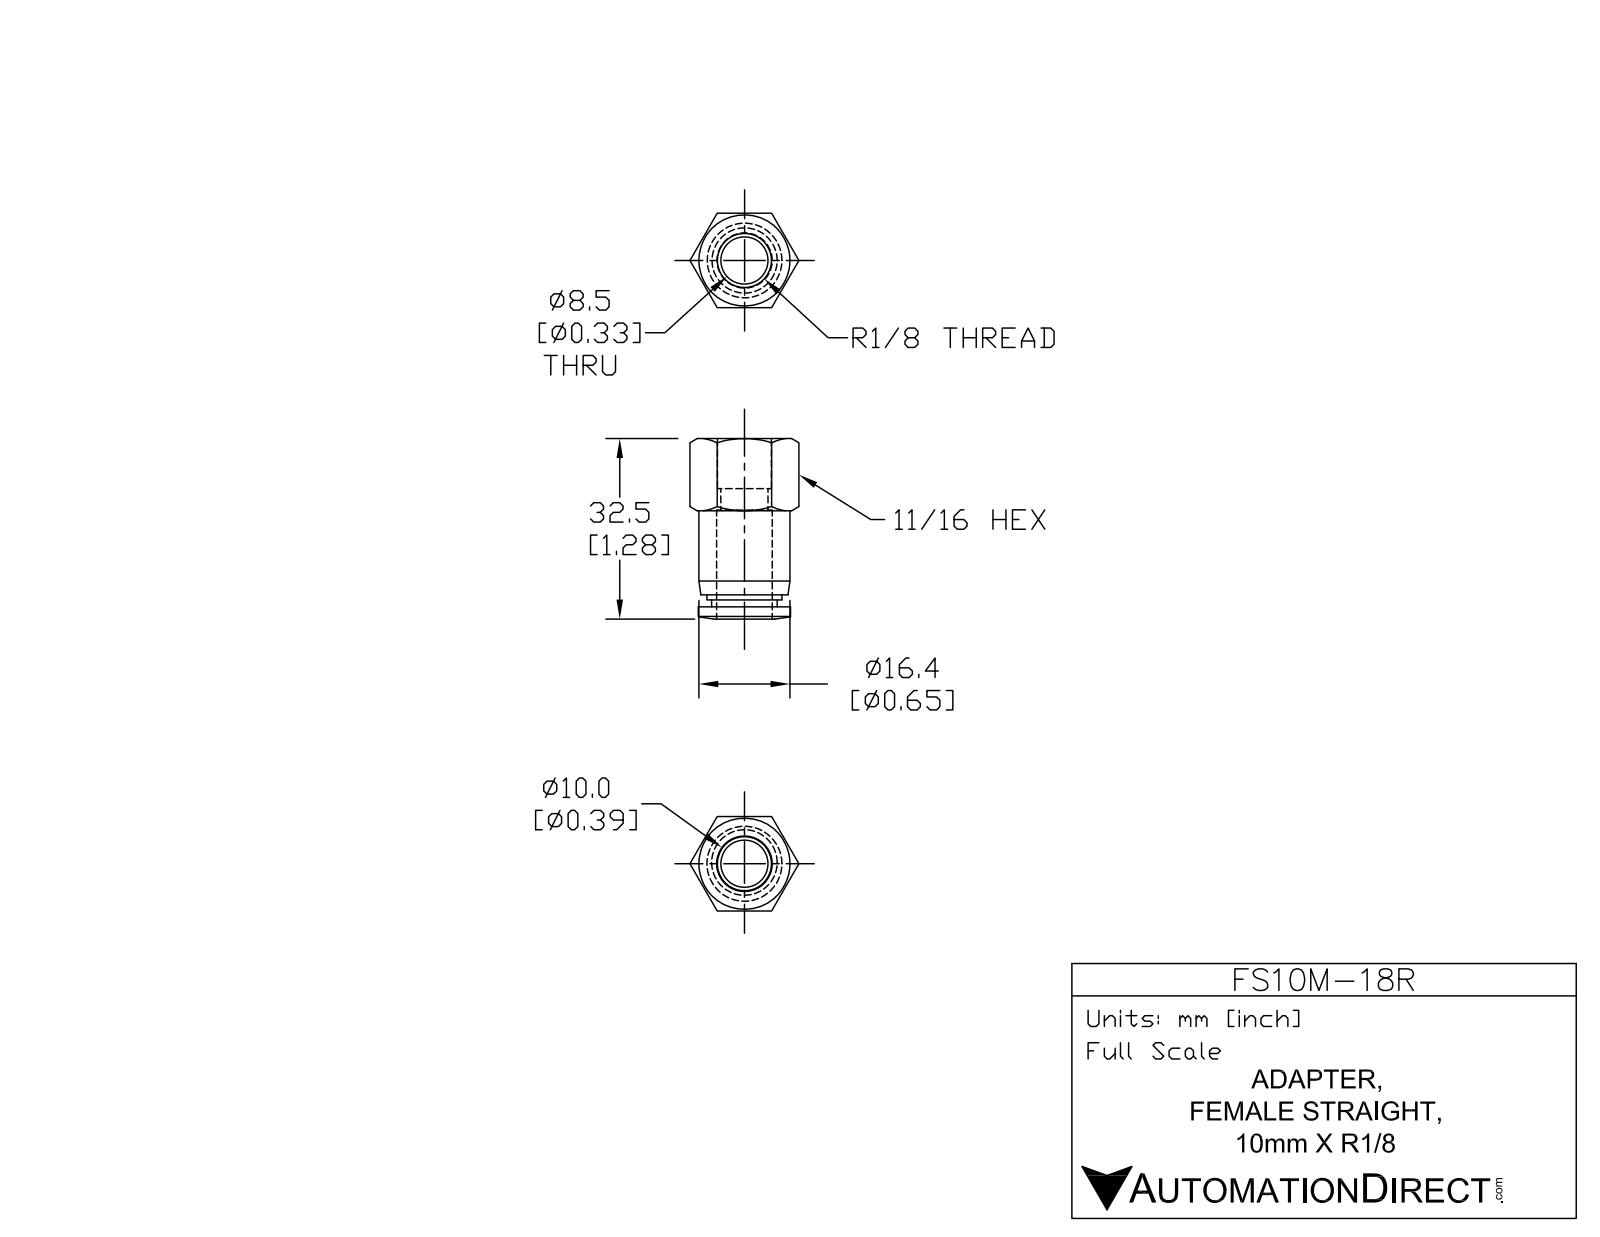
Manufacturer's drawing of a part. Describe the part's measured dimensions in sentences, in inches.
The part is named "FS10M-18R". Its 3-D file was written by "SolidWorks 2015 (AUTOMOTIVE_DESIGN)". It is 1 solid with 50 faces: 14 planar, 12 cylindrical and 24 other. Overall it measures 1.281 by 0.773 by 0.669 inches. Its volume is 0.284 cubic inches and its surface area 5.084 square inches. Round holes: 1 of diameter 0.335, 1 of diameter 0.406. Round bosses or shafts: 1 of diameter 0.654, 1 of diameter 0.646, 1 of diameter 0.531, 1 of diameter 0.465. The main face-to-face distances are 0.669, 1.195, 1.11, 0.085, 1.146, 0.035, 0.049, 0.51, 0.6, 0.636.
